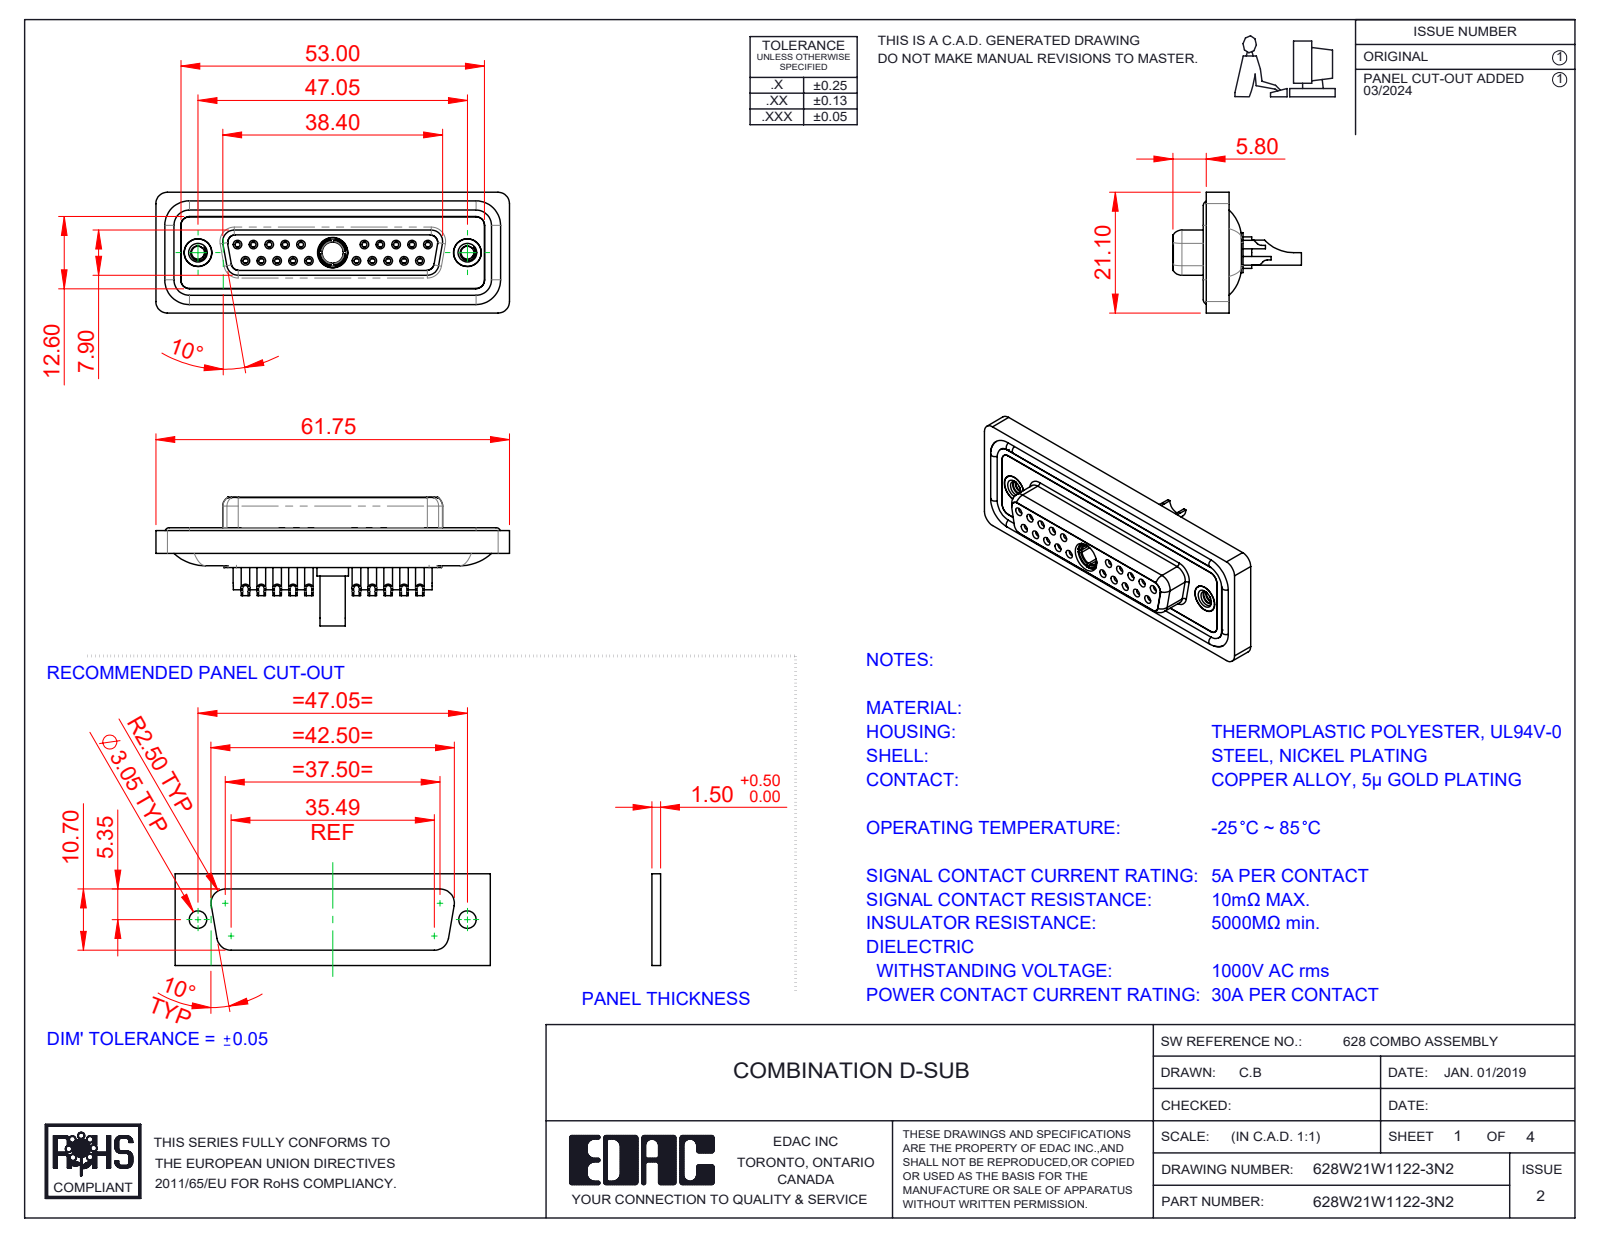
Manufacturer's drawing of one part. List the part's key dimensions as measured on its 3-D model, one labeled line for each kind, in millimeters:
Part name (STEP PRODUCT): 628Combo Waterproof Housing_25 Contacts; Power Socket_30A SC; 628Combo Threaded Rivet_2; 628Combo Housing_21W1 (+5 more)
STEP written by: SolidWorks 2023 (CONFIG_CONTROL_DESIGN)
Units: millimetres
Bodies: 29 solids, 1566 faces (477 planar, 634 cylindrical, 455 other)
Overall size (bounding box): 61.75 × 22.45 × 21.1
Volume: 8 439 mm³ · Surface area: 14 320 mm²
Round holes (diameter × count): ⌀0.9 ×20, ⌀1 ×20, ⌀1.1 ×20, ⌀1.5 ×20, ⌀2 ×20, ⌀1.6 ×10, ⌀1.7 ×10, ⌀4.85 ×3, ⌀2.26 ×2, ⌀4 ×2, ⌀4.05 ×2, ⌀5 ×2
Round bosses / shafts (diameter × count): ⌀2.2 ×20, ⌀1.6 ×14, ⌀4.95 ×2, ⌀4.8 ×2, ⌀5.5 ×1, ⌀5.2 ×1, ⌀4.96 ×1, ⌀4.75 ×1
Partial cylindrical surfaces — rounded edges, fillets, slot ends (radius × count): R1.5 ×22, R2 ×18, R1.35 ×8, R1.6 ×8, R1 ×6, R0.25 ×4, R0.5 ×4, R0.6 ×4
Main face-to-face distances: 0.4, 1.8, 7.45, 5.65, 6.6, 0.5, 1.6, 7.05, 2.9, 1.1
Hole centre spacings: 3.16, 2.77, 5.54, 5.03, 8.31, 7.48, 16.62, 19.39
